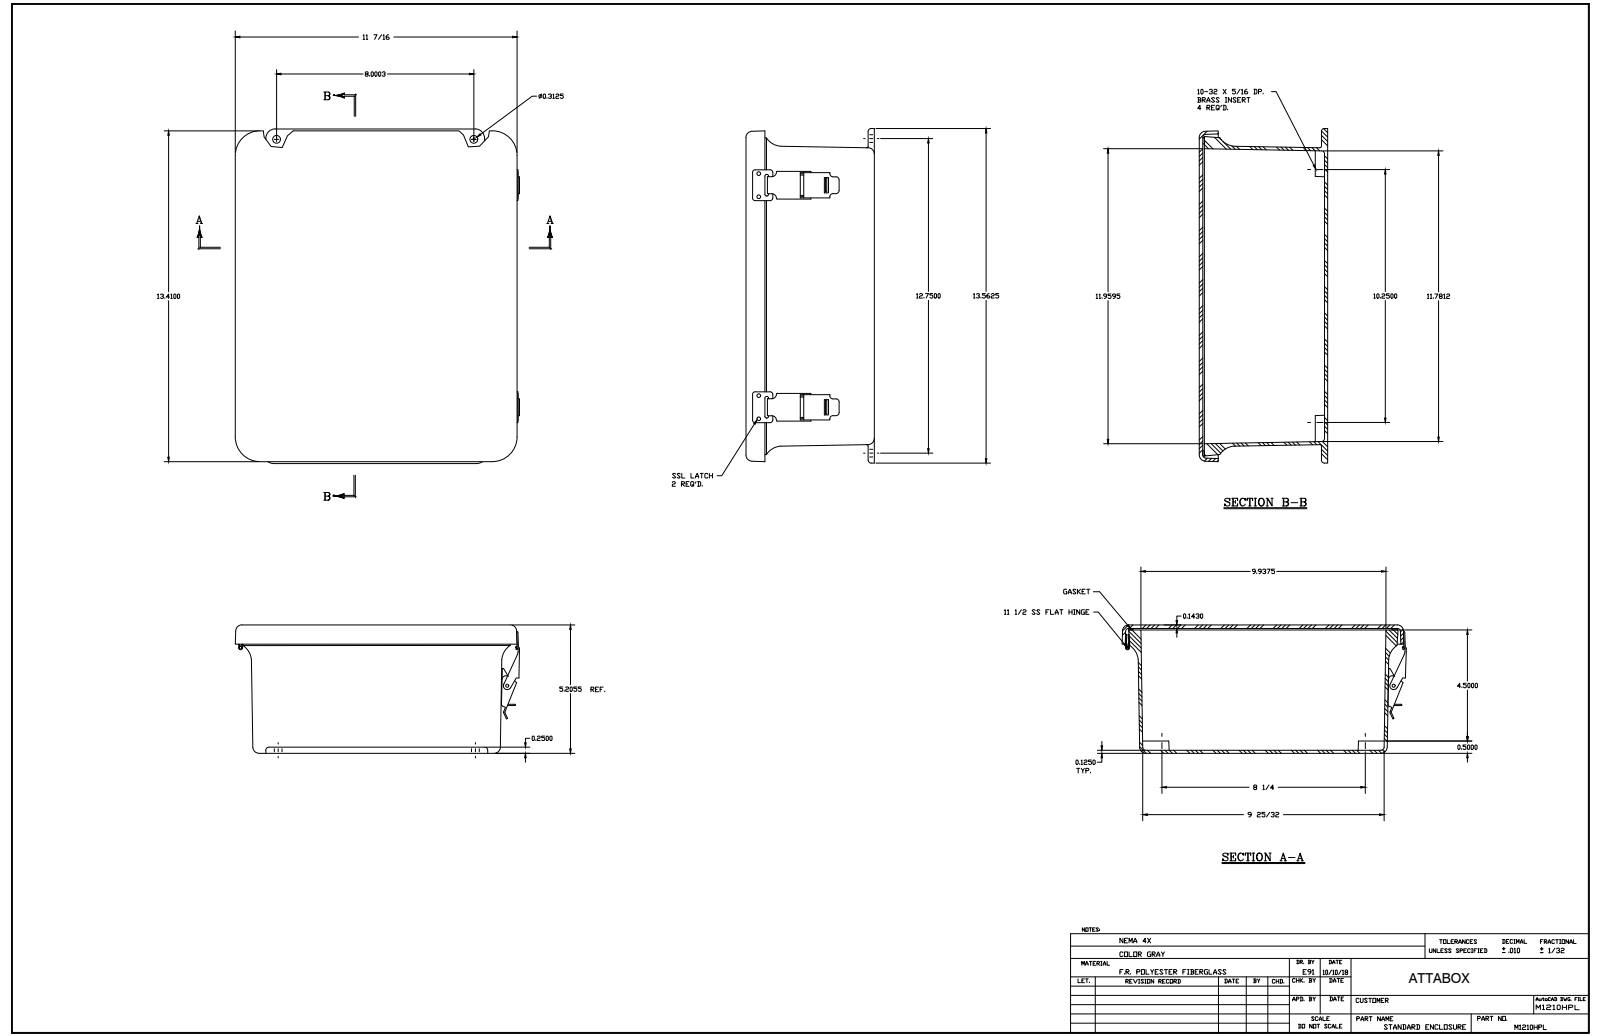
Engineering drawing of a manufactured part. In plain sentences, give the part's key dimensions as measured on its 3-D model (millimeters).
The part is named "M1210HPL". Its 3-D file was written by "SolidWorks 2018 (AUTOMOTIVE_DESIGN)". It is 38 solids with 979 faces: 423 planar, 409 cylindrical and 147 other. Overall it measures 344.5 by 293.3 by 132.9 millimeters. Its volume is 1 431 000 cubic millimeters and its surface area 772 900 square millimeters. Round holes: 20 of diameter 3.6, 8 of diameter 2.6, 8 of diameter 3.3, 5 of diameter 3.9, 4 of diameter 3.3, 4 of diameter 4, 4 of diameter 5.5, 2 of diameter 3.4, 2 of diameter 9.5, 1 of diameter 2.2, 1 of diameter 2.2, 1 of diameter 3.4. Round bosses or shafts: 12 of diameter 3.2, 8 of diameter 6.4, 4 of diameter 6.9, 4 of diameter 3.2, 1 of diameter 7.6, 1 of diameter 4.3, 1 of diameter 3.9, 1 of diameter 3. Partial cylindrical surfaces (rounded edges, fillets, slot ends): 22 of radius 3.2, 20 of radius 0.4, 20 of radius 0.8, 16 of radius 1.1, 12 of radius 0.8, 9 of radius 0.6, 8 of radius 6.4, 6 of radius 1.5. The main face-to-face distances are 3.6, 129.3, 132.9, 3.2, 126.1, 129.7, 3.2, 123.8, 127, 2.3. The hole center spacings are 228.6, 23.8, 19.1, 229.4, 37.3, 55.7, 92.1, 92.1.
